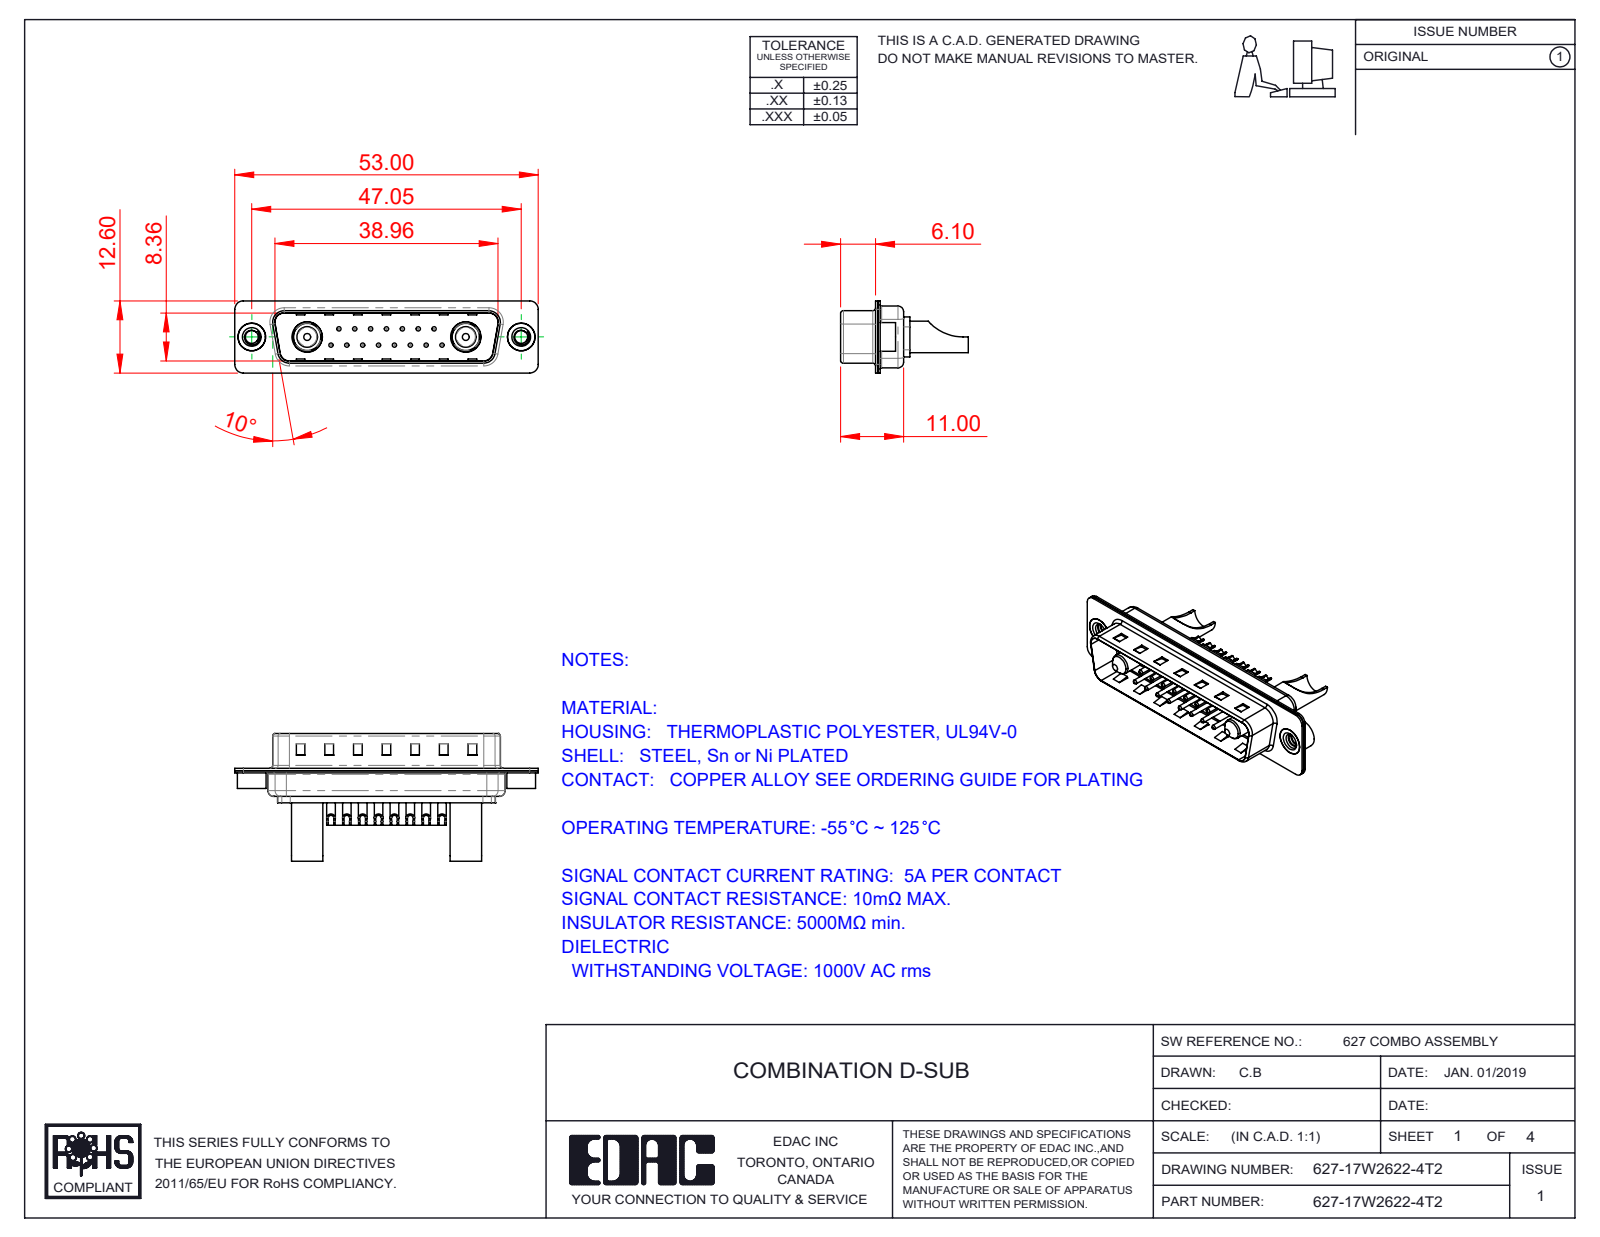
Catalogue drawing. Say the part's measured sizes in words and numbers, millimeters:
The part is named "Power Pin_40A SC; 627-17W2622-4T2; 627Combo Contact Row 2_22; 627Combo Contact Row 1_22 (+4 more)". Its 3-D file was written by "SolidWorks 2016 (CONFIG_CONTROL_DESIGN)". It is 24 solids with 1017 faces: 330 planar, 417 cylindrical and 270 other. Overall it measures 53 by 22.3 by 12.6 millimeters. Its volume is 2 959 cubic millimeters and its surface area 7 188 square millimeters. Round holes: 15 of diameter 0.75, 15 of diameter 1, 15 of diameter 1.6, 15 of diameter 2, 2 of diameter 2.26, 2 of diameter 4, 2 of diameter 4.6, 2 of diameter 4.8, 2 of diameter 4.85, 2 of diameter 5.3. Round bosses or shafts: 15 of diameter 1.5, 2 of diameter 5.5, 2 of diameter 5.2, 2 of diameter 5, 2 of diameter 4.9, 2 of diameter 4.75, 2 of diameter 3.75, 2 of diameter 3.6. Partial cylindrical surfaces (rounded edges, fillets, slot ends): 16 of radius 1.5, 12 of radius 2, 8 of radius 0.5, 8 of radius 1.6, 6 of radius 1, 4 of radius 0.25, 4 of radius 0.6, 4 of radius 0.65. The main face-to-face distances are 0.4, 0.82, 9.58, 8.76, 1.5, 5.2, 0.8, 1.22, 9.98, 0.42. The hole center spacings are 3.16, 2.77, 5.54, 8.31, 5.04, 7.49, 11.08, 5.03.
